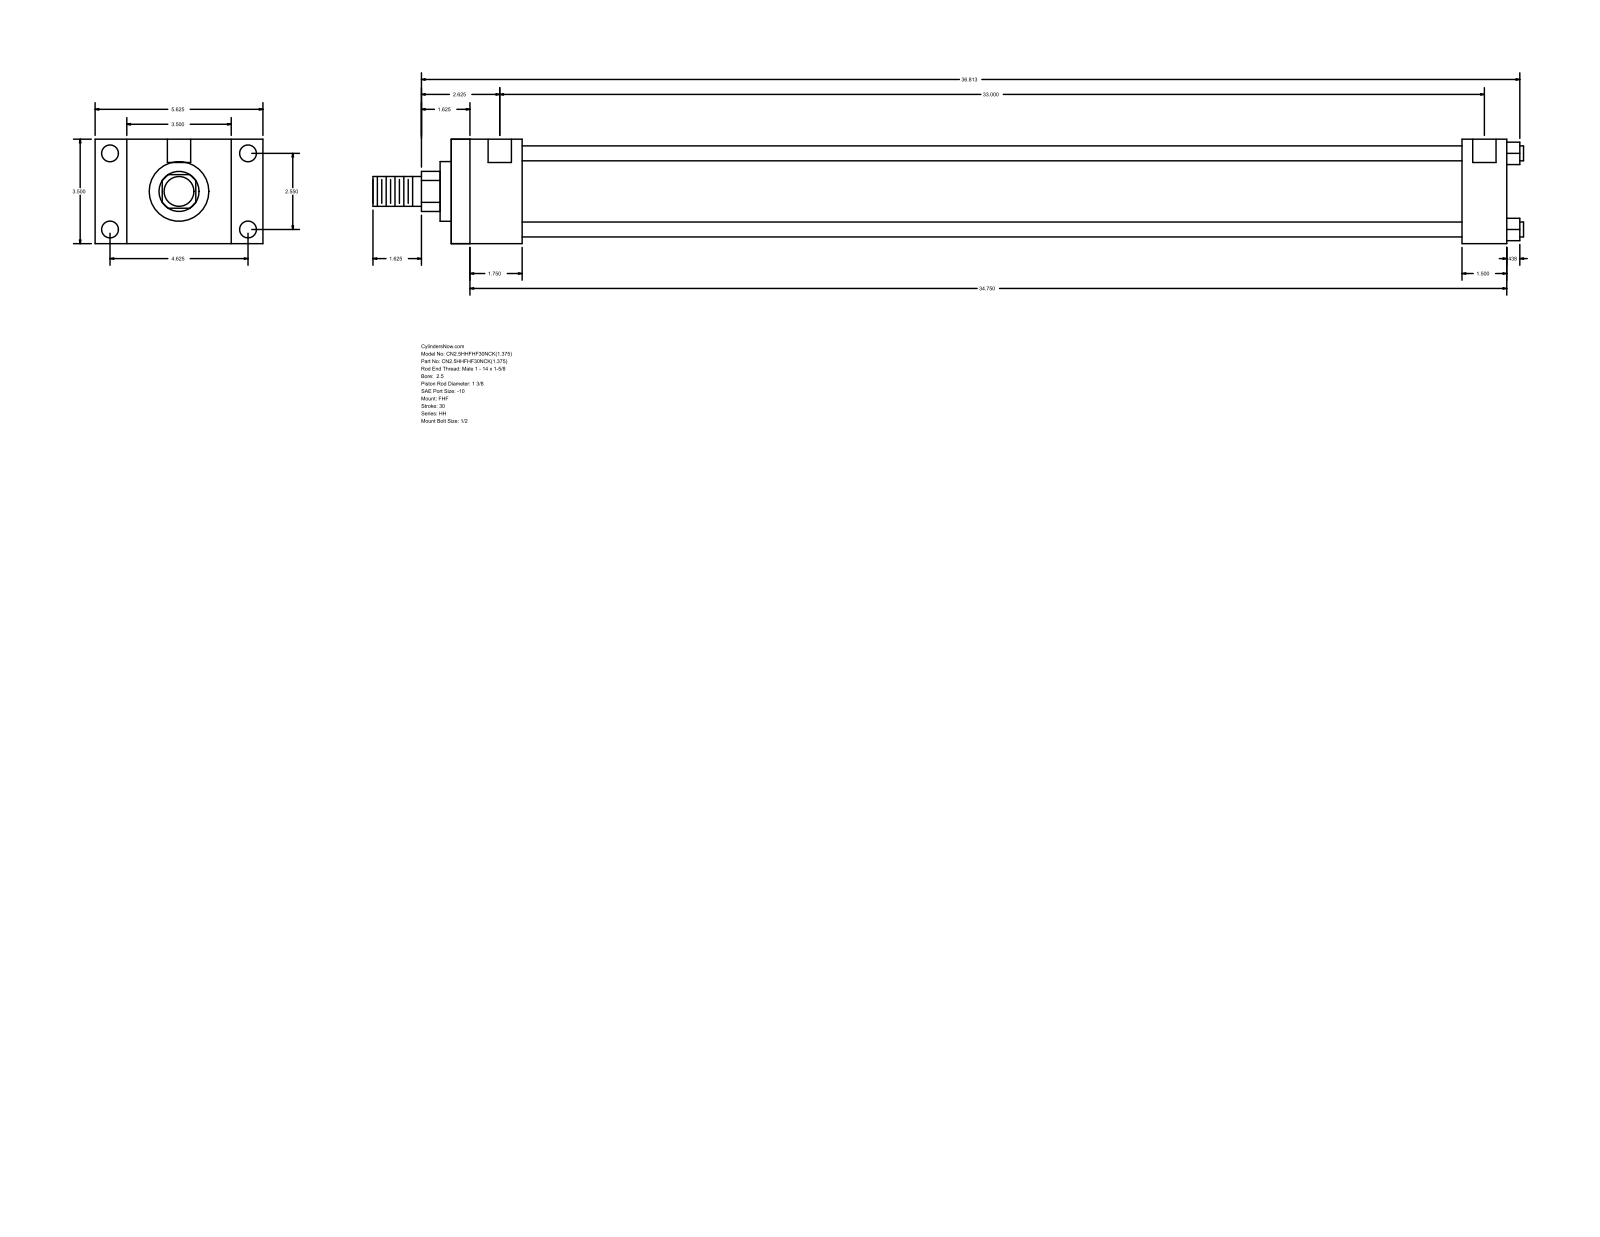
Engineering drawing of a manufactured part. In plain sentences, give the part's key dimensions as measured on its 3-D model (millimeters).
The part is named "HH_FHF__0250_1.375". Its 3-D file was written by "GSSL Pune (CONFIG_CONTROL_DESIGN)". It is 0 solids with 88 faces: 60 planar, 28 cylindrical and 0 other. Overall it measures 979.49 by 142.88 by 88.9 millimeters. Round holes: 4 of diameter 5.56, 4 of diameter 14.3, 2 of diameter 19.84. Round bosses or shafts: 4 of diameter 12.7, 1 of diameter 73.03, 1 of diameter 50.8, 1 of diameter 34.92, 1 of diameter 25.4. Partial cylindrical surfaces (rounded edges, fillets, slot ends): 1 of radius 17.06. The main face-to-face distances are 88.9, 60.32, 26.99, 115.89, 898.52, 838.2, 142.88, 860.43, 800.11, 38.09. The hole center spacings are 1.58, 64.76, 117.48, 134.15, 839.79, 841.37, 838.21.
